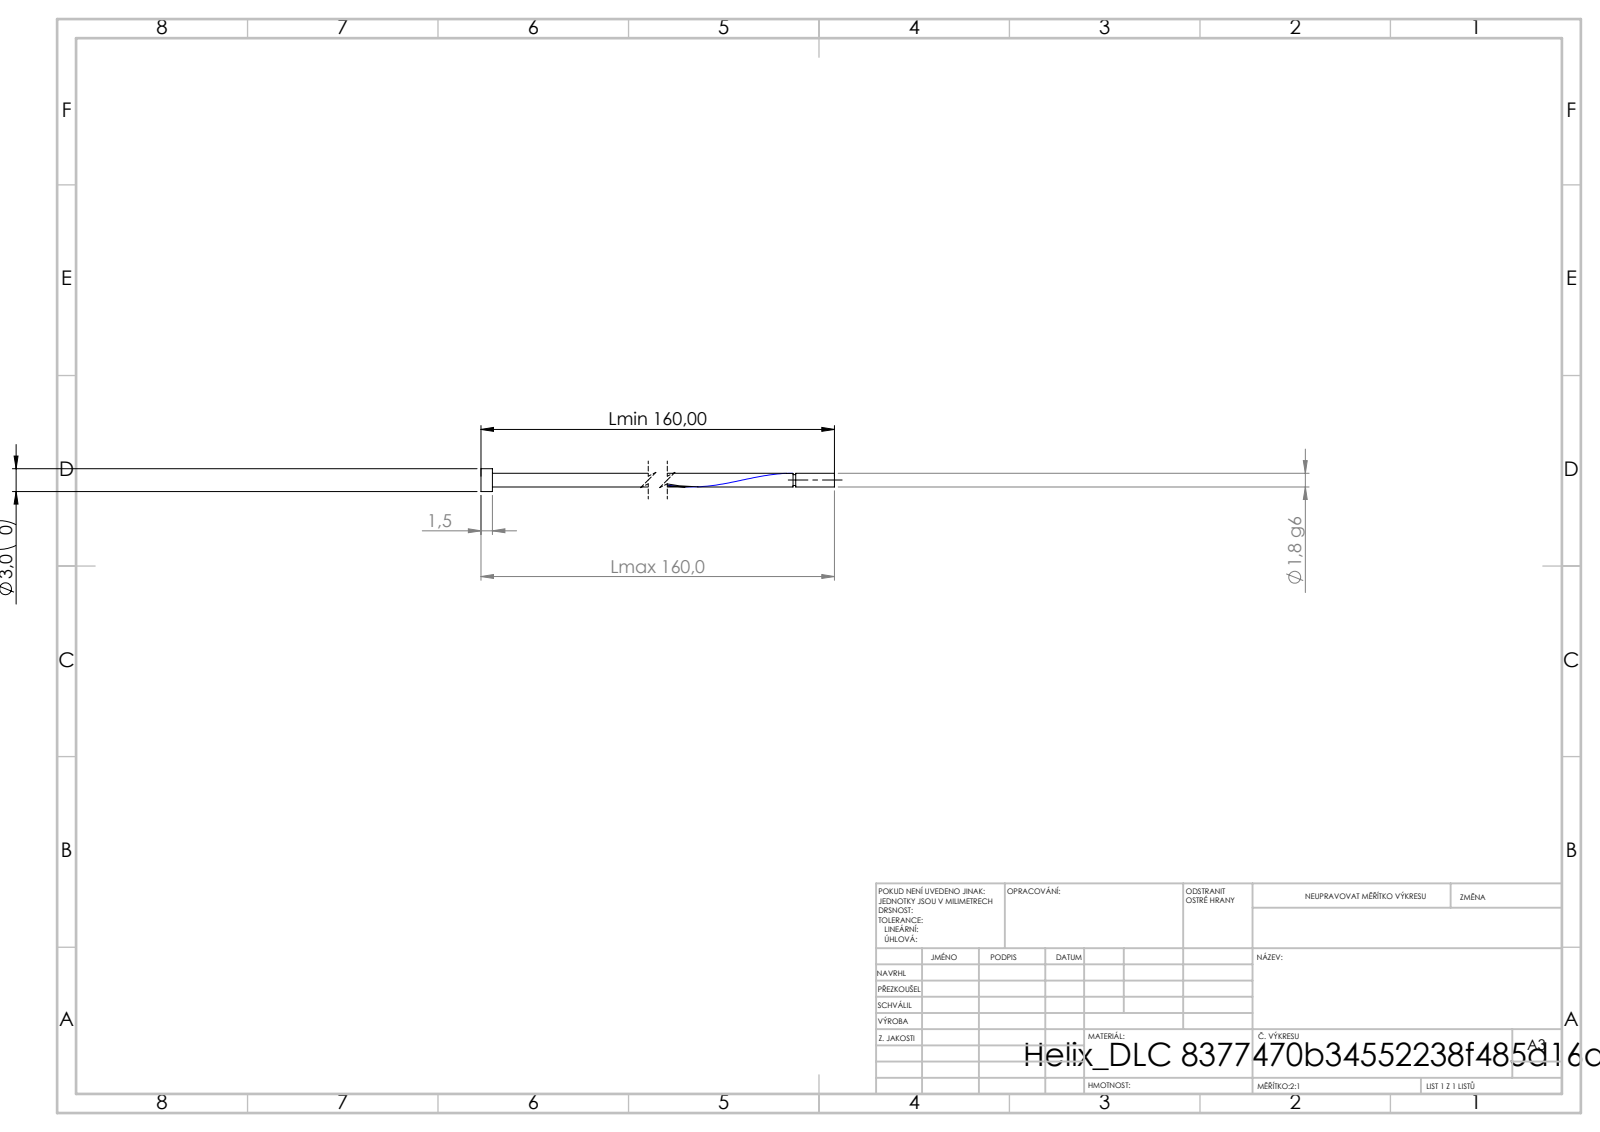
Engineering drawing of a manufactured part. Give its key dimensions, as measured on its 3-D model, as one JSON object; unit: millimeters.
{"step_written_by": "SolidWorks 2019 (CONFIG_CONTROL_DESIGN)", "units": "millimeters", "bodies": {"solids": 1, "faces": 16, "planar": 6, "cylindrical": 9, "other": 1}, "overall_size": [160, 3, 3], "volume_mm3": 500, "surface_area_mm2": 1241, "round_bosses_or_shafts": [[3, 1], [1.8, 1], [1.44, 1]], "face_to_face_distances": [1.5, 160, 158.5, 154.93, 153.43, 5.07, 154.57, 153.07, 0.36, 5.43]}
